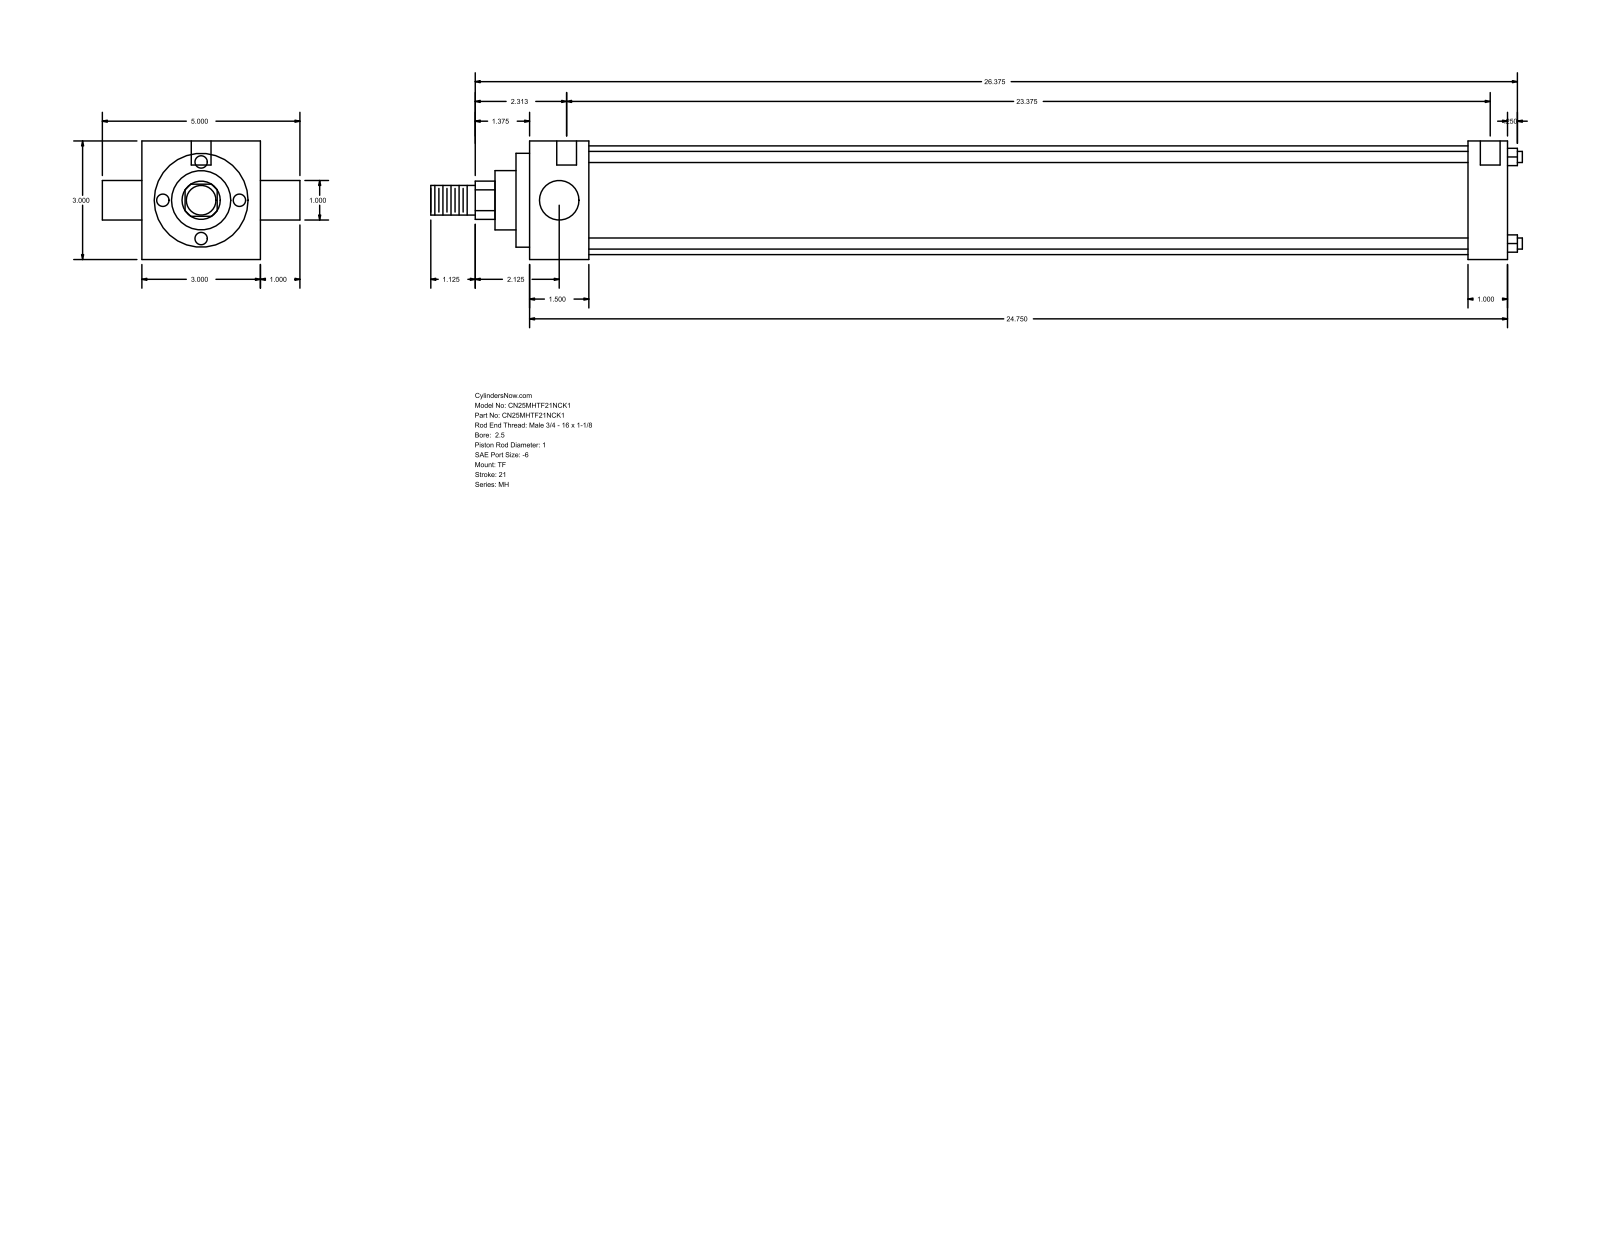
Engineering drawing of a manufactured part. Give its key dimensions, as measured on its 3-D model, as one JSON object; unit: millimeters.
{"part_name": "MH_TF__0250_1", "step_written_by": "GSSL Pune (CONFIG_CONTROL_DESIGN)", "units": "millimeters", "bodies": {"solids": 0, "faces": 86, "planar": 61, "cylindrical": 25, "other": 0}, "overall_size": [701.67, 127, 76.2], "round_holes": [[5.56, 3], [12.7, 2]], "round_bosses_or_shafts": [[7.14, 4], [25.4, 2], [69.85, 1], [60.33, 1], [38.1, 1], [19.05, 1]], "partial_cylinders_radius": [[12.29, 1]], "face_to_face_distances": [76.2, 628.66, 38.11, 590.55, 603.25, 565.14, 25.41, 8.73, 46.84, 611.98], "hole_center_spacings": [3.18, 4.76, 593.72, 596.9, 598.48, 601.66]}
